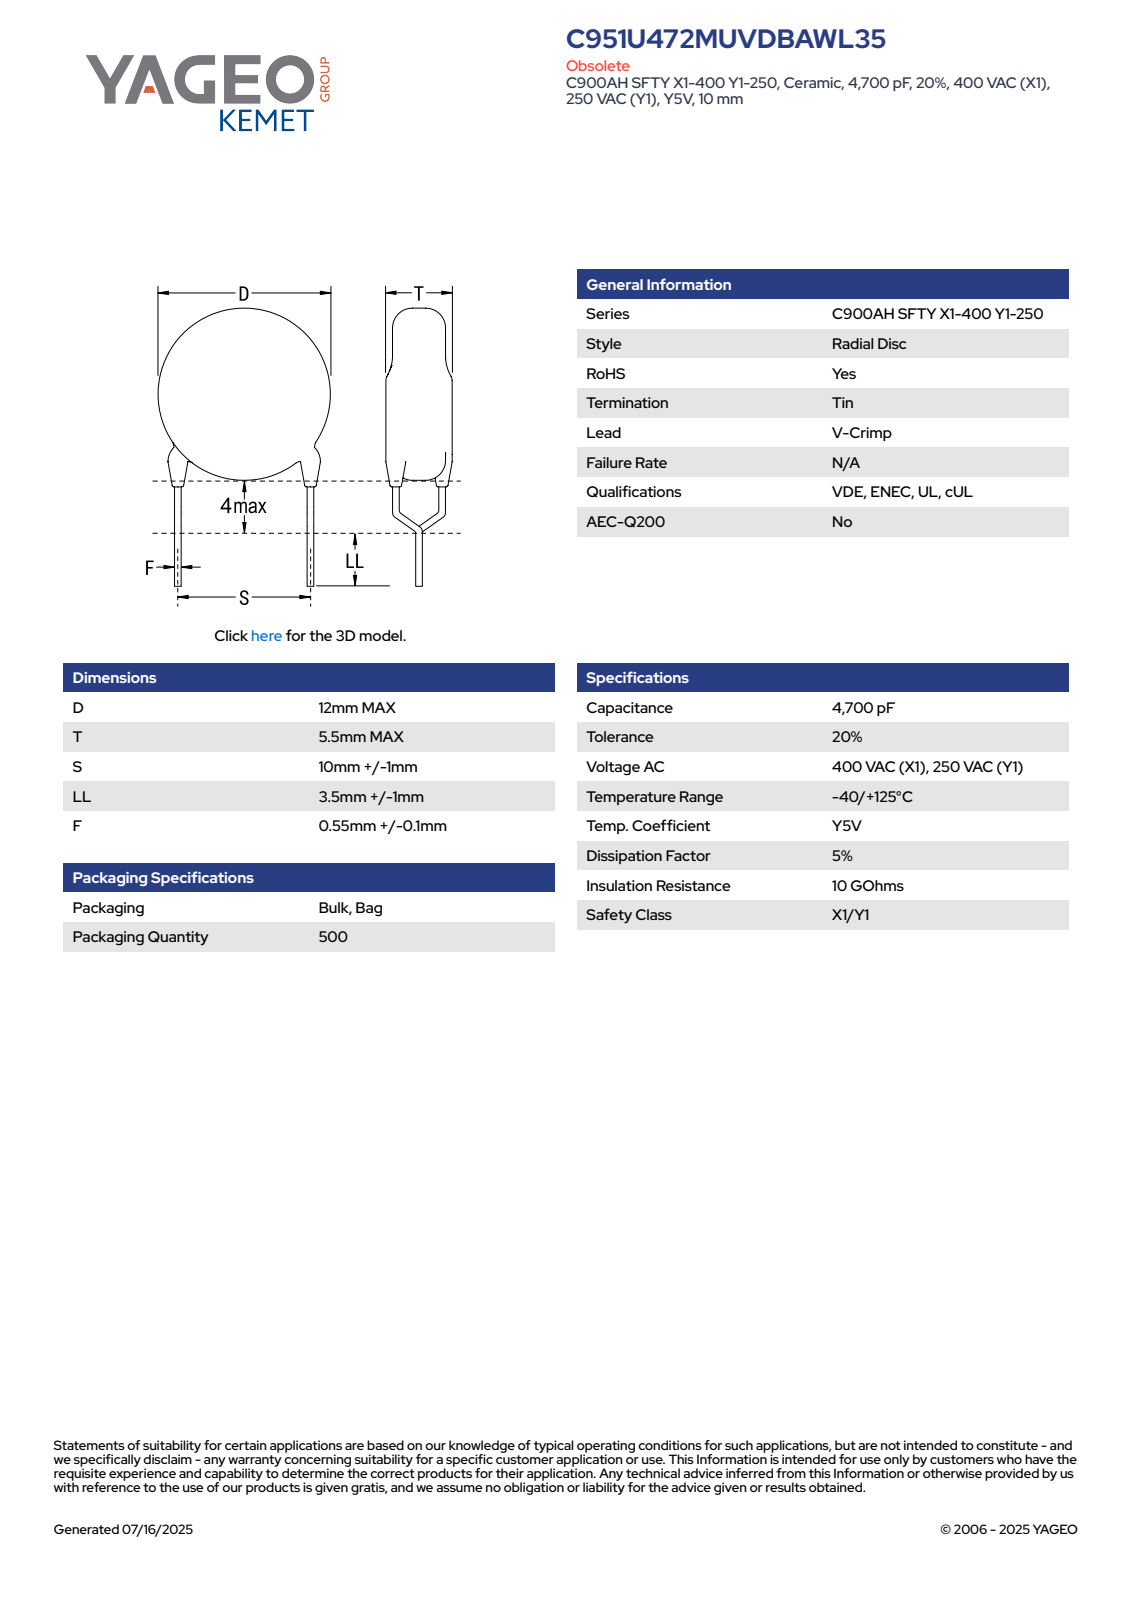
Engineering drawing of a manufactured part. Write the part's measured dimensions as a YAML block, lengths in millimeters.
part_name: "CCD_VCC900_D12T5.5S10LL4.5F0.65"
step_written_by: "SolidWorks 2014 (AUTOMOTIVE_DESIGN)"
units: millimeters
bodies: {solids: 5, faces: 93, planar: 65, cylindrical: 16, other: 12}
overall_size: [20.3, 12, 5.5]
volume: 616
surface_area: 462
round_bosses_or_shafts:
  - {diameter: 0.65, count: 6}
  - {diameter: 12, count: 1}
face_to_face_distances: [5.5, 7.4, 15.08, 7.68, 13.52, 6.12, 1.56, 0.42, 0.38, 1.26]
